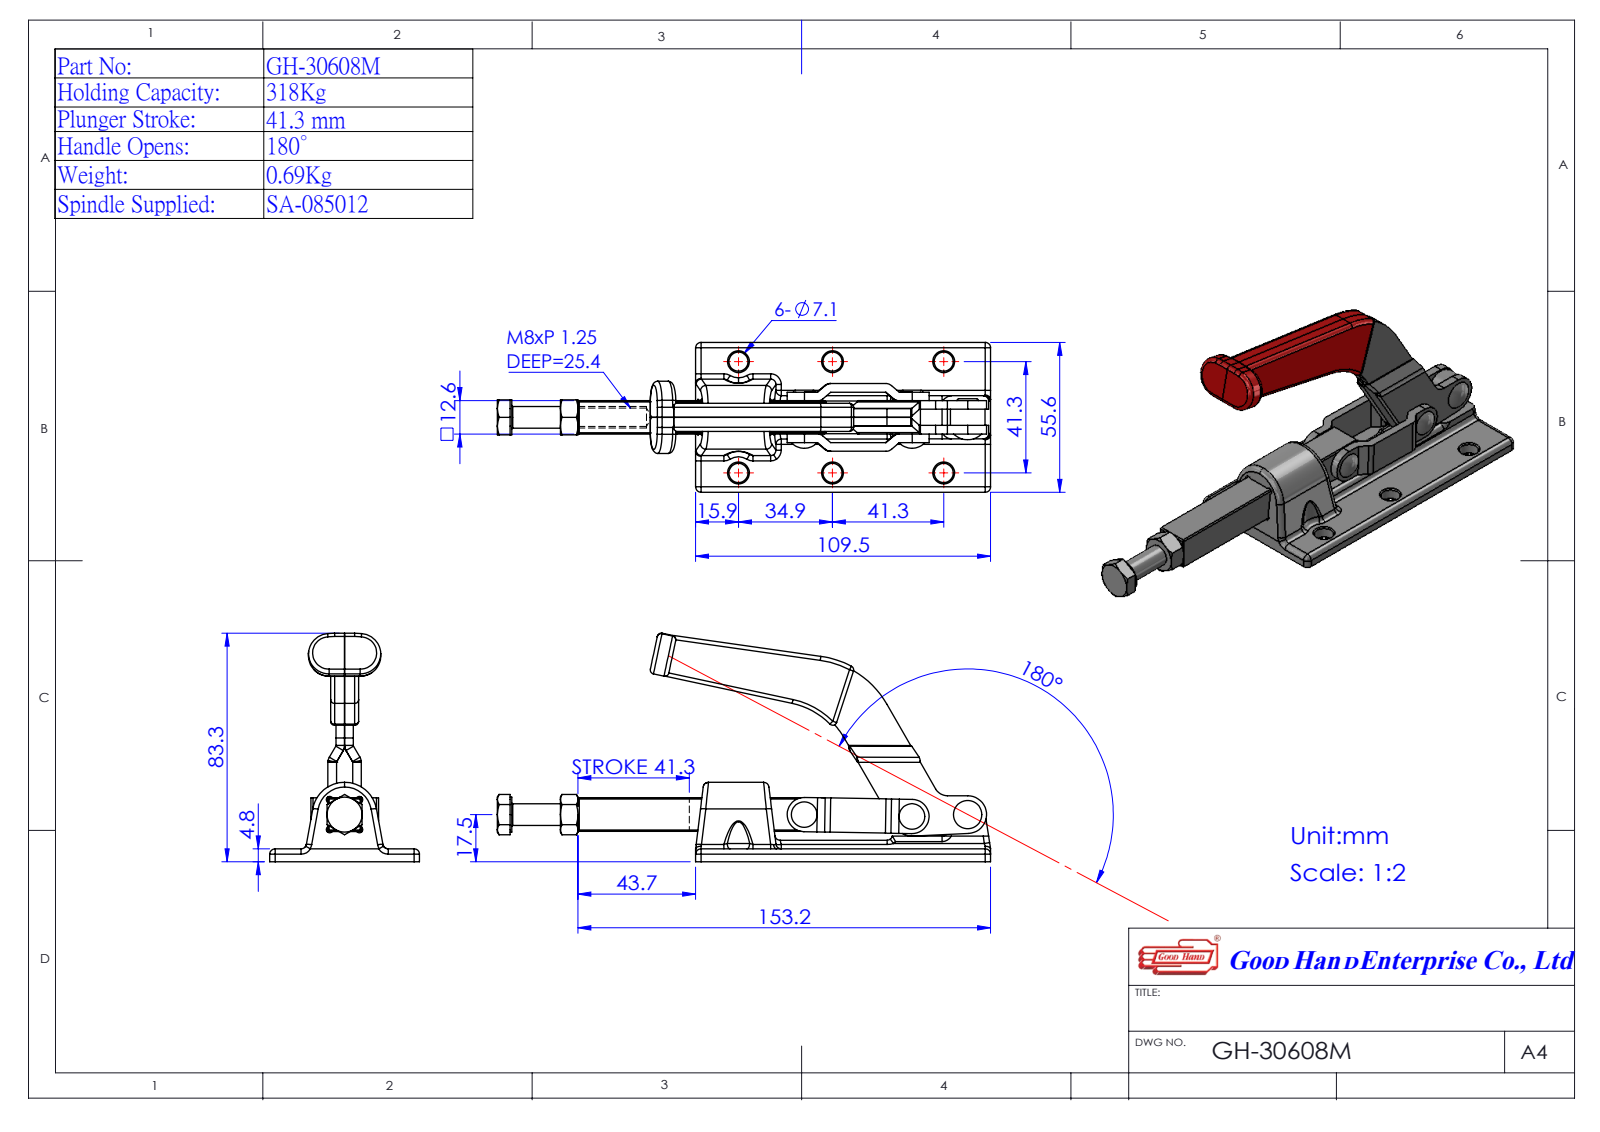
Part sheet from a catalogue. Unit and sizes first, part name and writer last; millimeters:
Units: millimetres
Overall size (bounding box): 183.09 × 85.1 × 55.6
Round holes (diameter × count): ⌀7.1 ×6, ⌀6.3 ×1, ⌀6.8 ×1
Round bosses / shafts (diameter × count): ⌀6.3 ×2, ⌀8 ×1
Partial cylindrical surfaces — rounded edges, fillets, slot ends (radius × count): R3.2 ×8, R0.5 ×4, R3.7 ×4, R6.35 ×2, R7.64 ×2, R8 ×2, R5 ×1, R6.5 ×1
Main face-to-face distances: 4.8, 3.2, 12.5, 3.25, 1.05, 11.45, 9.25, 2.2, 8.2, 12.45
Hole centre spacings: 41.3, 34.9, 54.07, 58.41, 76.2, 86.67
Volume: 91 452 mm³ · Surface area: 40 473 mm²
Bodies: 5 solids, 293 faces (178 planar, 77 cylindrical, 38 other)
Part name (STEP PRODUCT): 430608M13-1^GH-30608M-1; 3302713-1^GH-30608M-1; GH-30608M-1; Group1^GH-30608M-1 (+2 more)
STEP written by: SolidWorks 2016 (AUTOMOTIVE_DESIGN)
